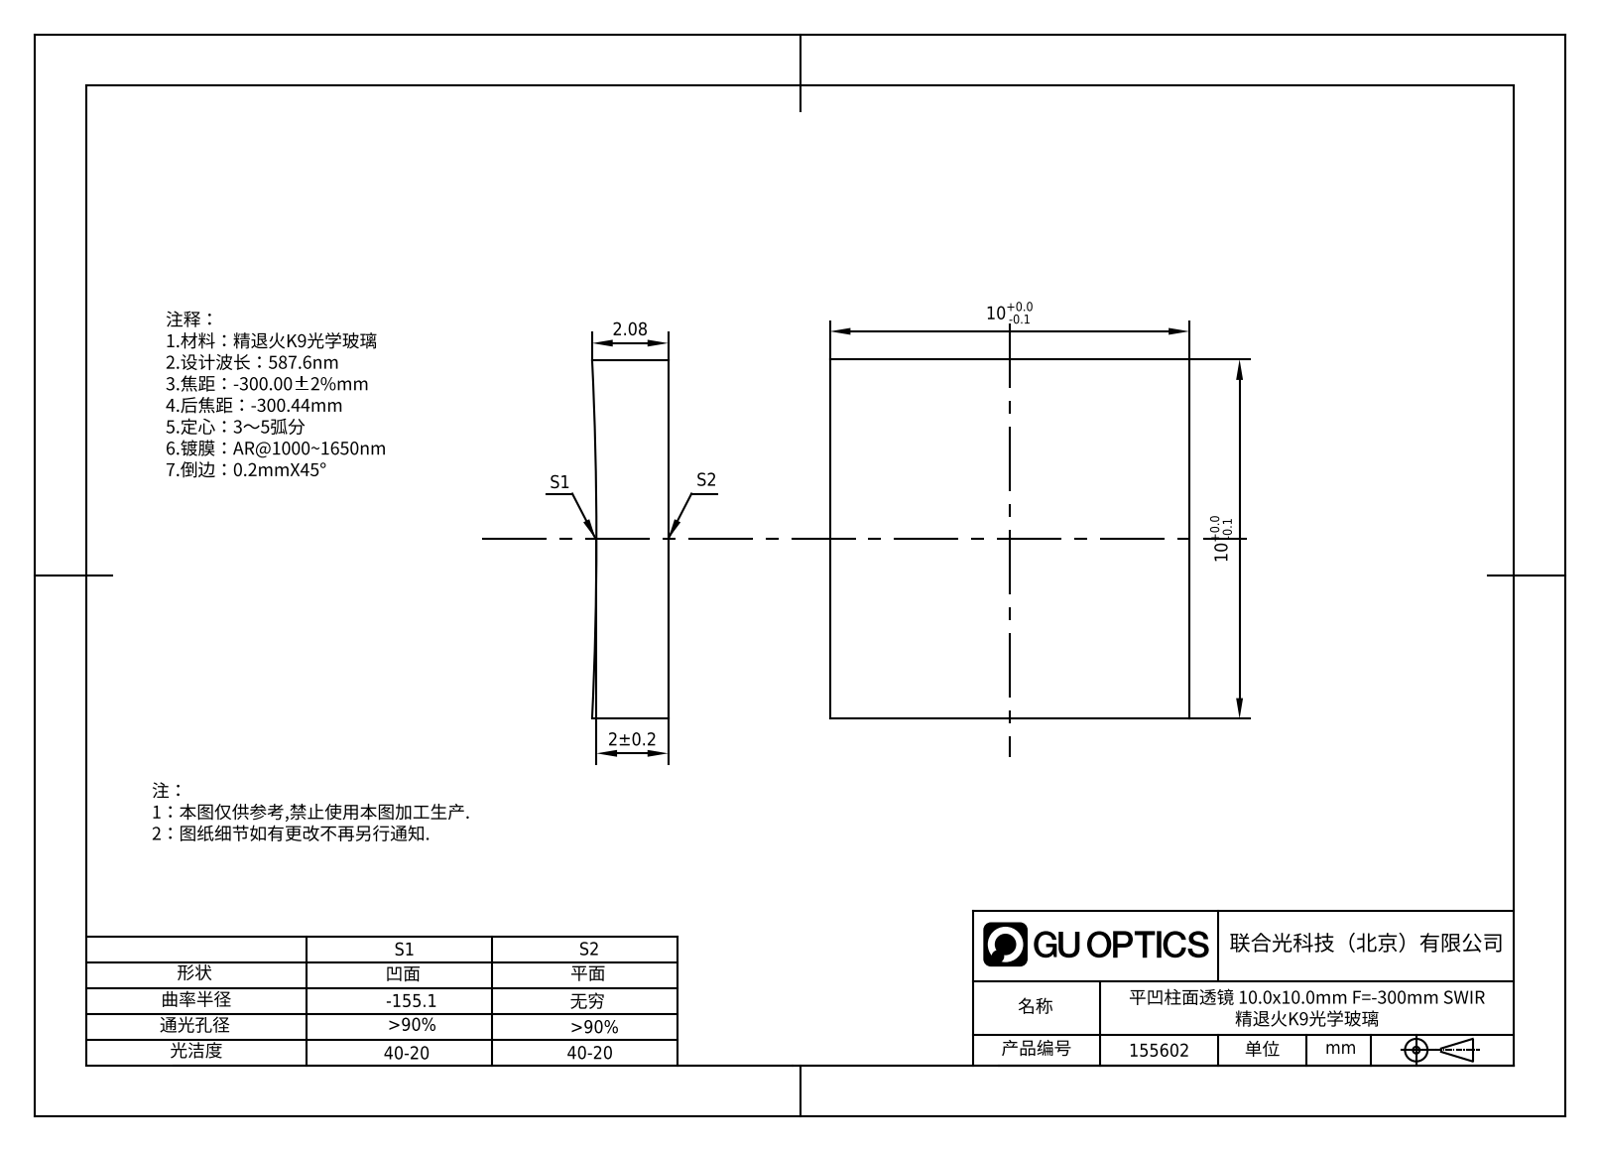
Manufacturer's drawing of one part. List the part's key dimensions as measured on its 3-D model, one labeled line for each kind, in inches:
Part name (STEP PRODUCT): 155572
STEP written by: SolidWorks 2020 (CONFIG_CONTROL_DESIGN)
Units: inches
Bodies: 1 solid, 6 faces (5 planar, 1 cylindrical, 0 other)
Overall size (bounding box): 0.394 × 0.394 × 0.082
Volume: 0.012 in³ · Surface area: 0.437 in²
Partial cylindrical surfaces — rounded edges, fillets, slot ends (radius × count): R6.106 ×1
Main face-to-face distances: 0.394
